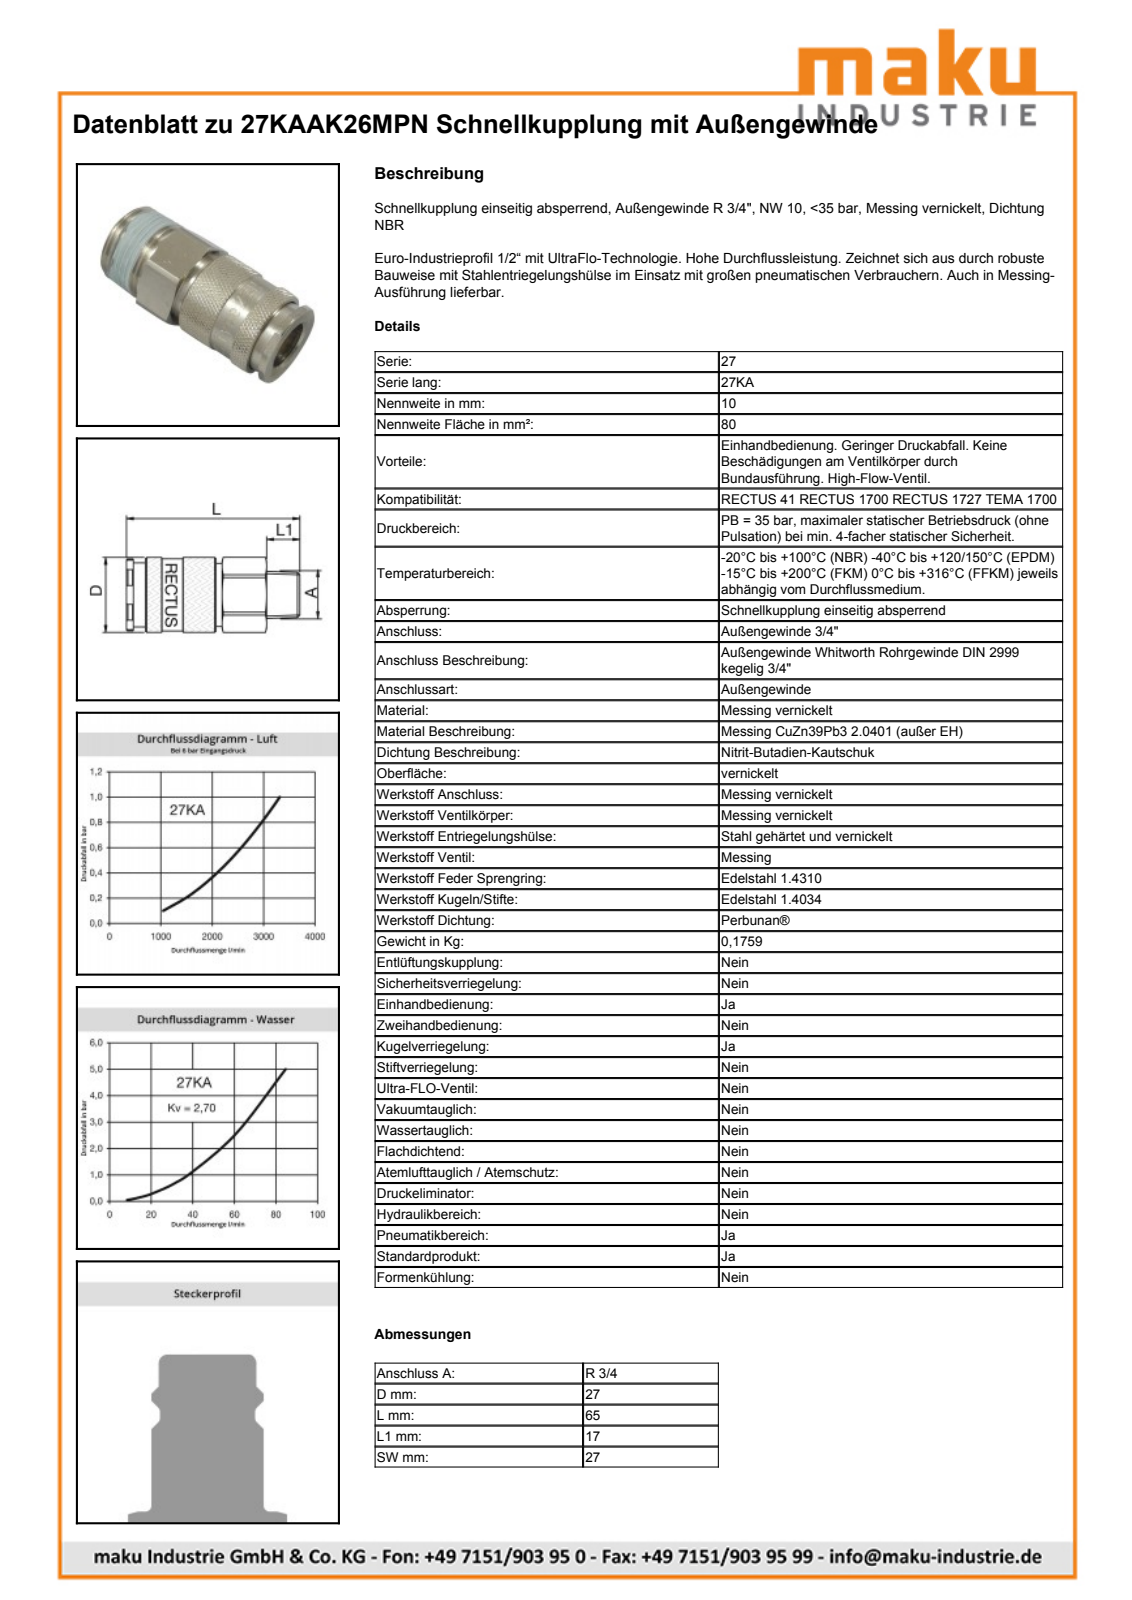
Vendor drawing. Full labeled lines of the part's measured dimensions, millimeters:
Part name (STEP PRODUCT): D110042
STEP written by: Autodesk Inventor 2013 (AUTOMOTIVE_DESIGN)
Units: millimetres
Bodies: 1 solid, 486 faces (189 planar, 60 cylindrical, 237 other)
Overall size (bounding box): 64.55 × 30.27 × 28.81
Volume: 34 701 mm³ · Surface area: 10 315 mm²
Round holes (diameter × count): ⌀23.35 ×1, ⌀23.55 ×1
Round bosses / shafts (diameter × count): ⌀27.15 ×1, ⌀26 ×1, ⌀23.1 ×1, ⌀22.75 ×1, ⌀21.53 ×1
Partial cylindrical surfaces — rounded edges, fillets, slot ends (radius × count): R12.9 ×1, R15.22 ×1
Main face-to-face distances: 64.55, 27.02, 27, 26.98, 34.5, 30.05, 32.3, 2.2, 32.25, 6.8
